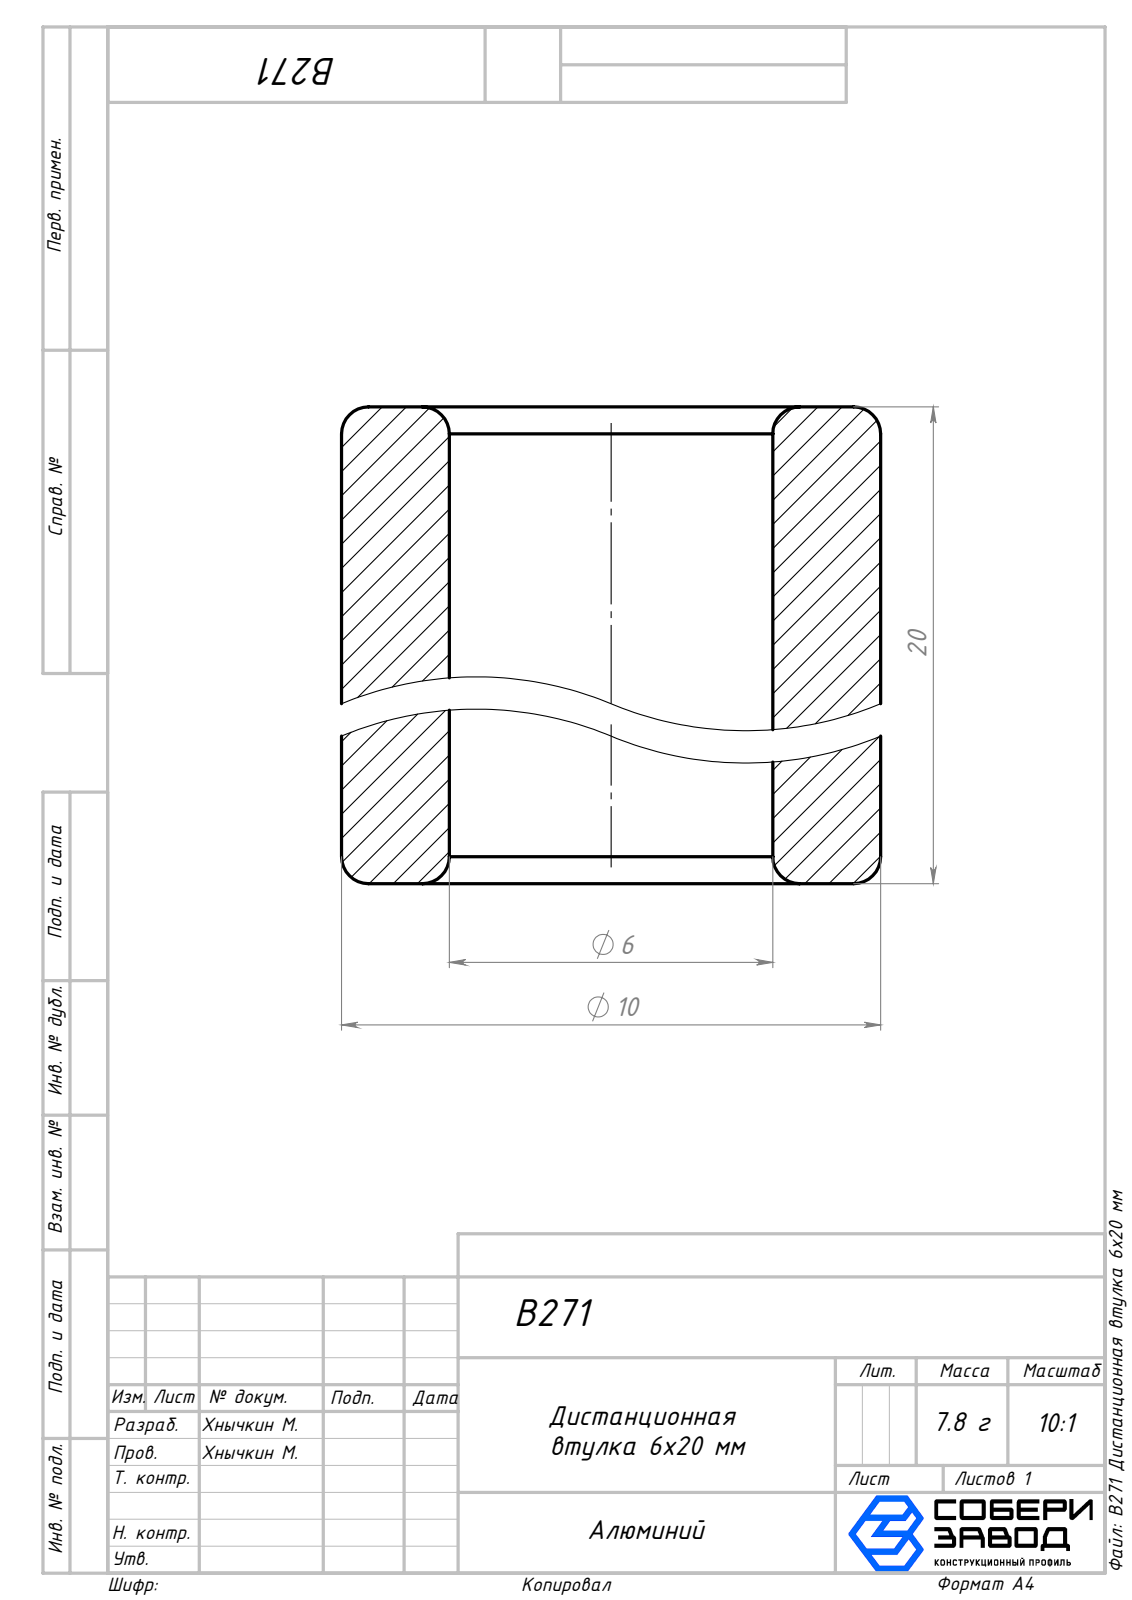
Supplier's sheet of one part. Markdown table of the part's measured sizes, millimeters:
| quantity | value |
| --- | --- |
| part name | B271 Дистанционная втулка 6x20 мм |
| STEP written by | SolidWorks 2026 (AUTOMOTIVE_DESIGN) |
| units | millimeters |
| bodies | 1 solid, 14 faces (2 planar, 4 cylindrical, 8 other) |
| overall size | 20 × 10 × 10 |
| volume | 1 000 mm³ |
| surface area | 1 084 mm² |
| round holes (diameter × count) | 6 × 1 |
| round bosses / shafts (diameter × count) | 10 × 1 |
| main face-to-face distances | 20 |
